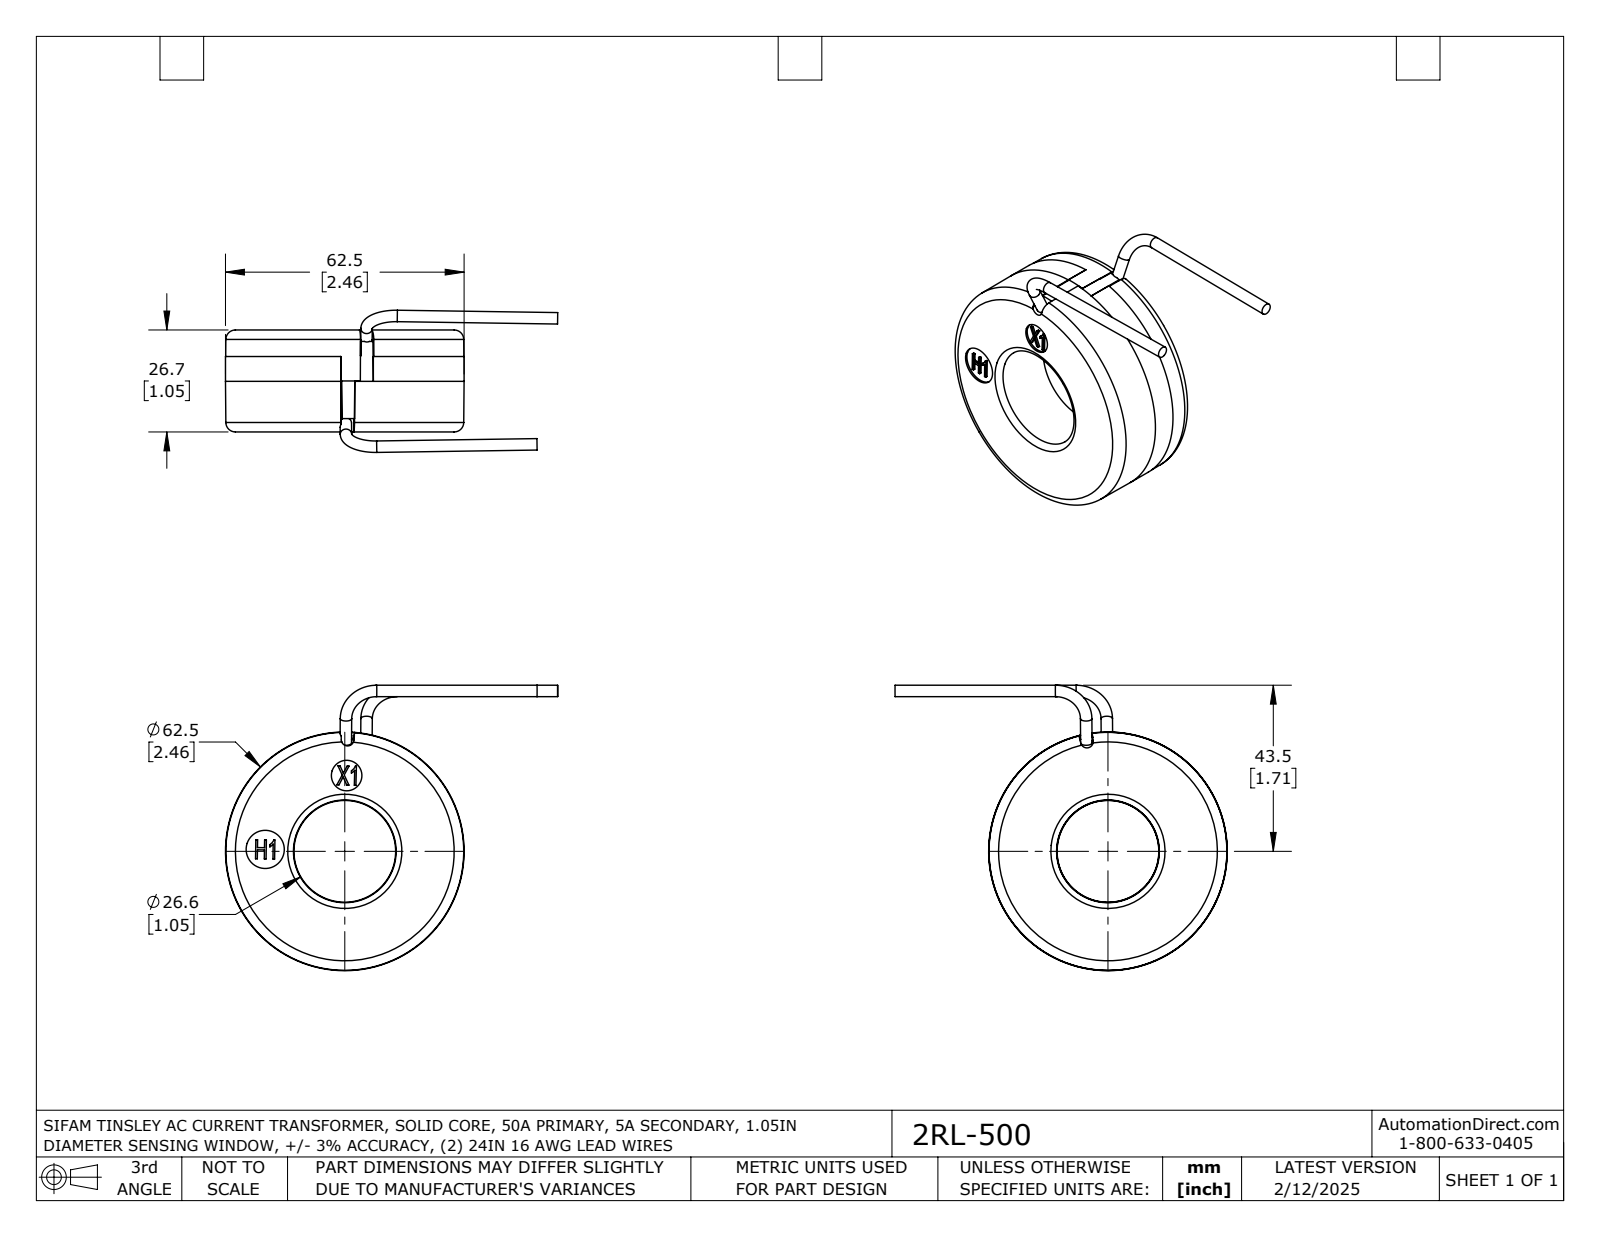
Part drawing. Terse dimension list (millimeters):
name: 2RL-500
written by: SolidWorks 2021 (AUTOMOTIVE_DESIGN)
unit: mm
bodies: 1 solid, 129 faces (62 planar, 18 cylindrical, 49 other)
size: 87.4 × 74.8 × 37.2
volume: 66 680 mm³; area: 13 430 mm²
holes: 1× ⌀8, 1× ⌀10, 1× ⌀60.5
bosses: 4× ⌀3, 1× ⌀62.5
face distances: 26.7, 0.5, 26.2, 0.5, 26.2, 19.8, 19.3, 19.3, 7, 13.4
hole spacings: 19.9, 20.9, 28.8
